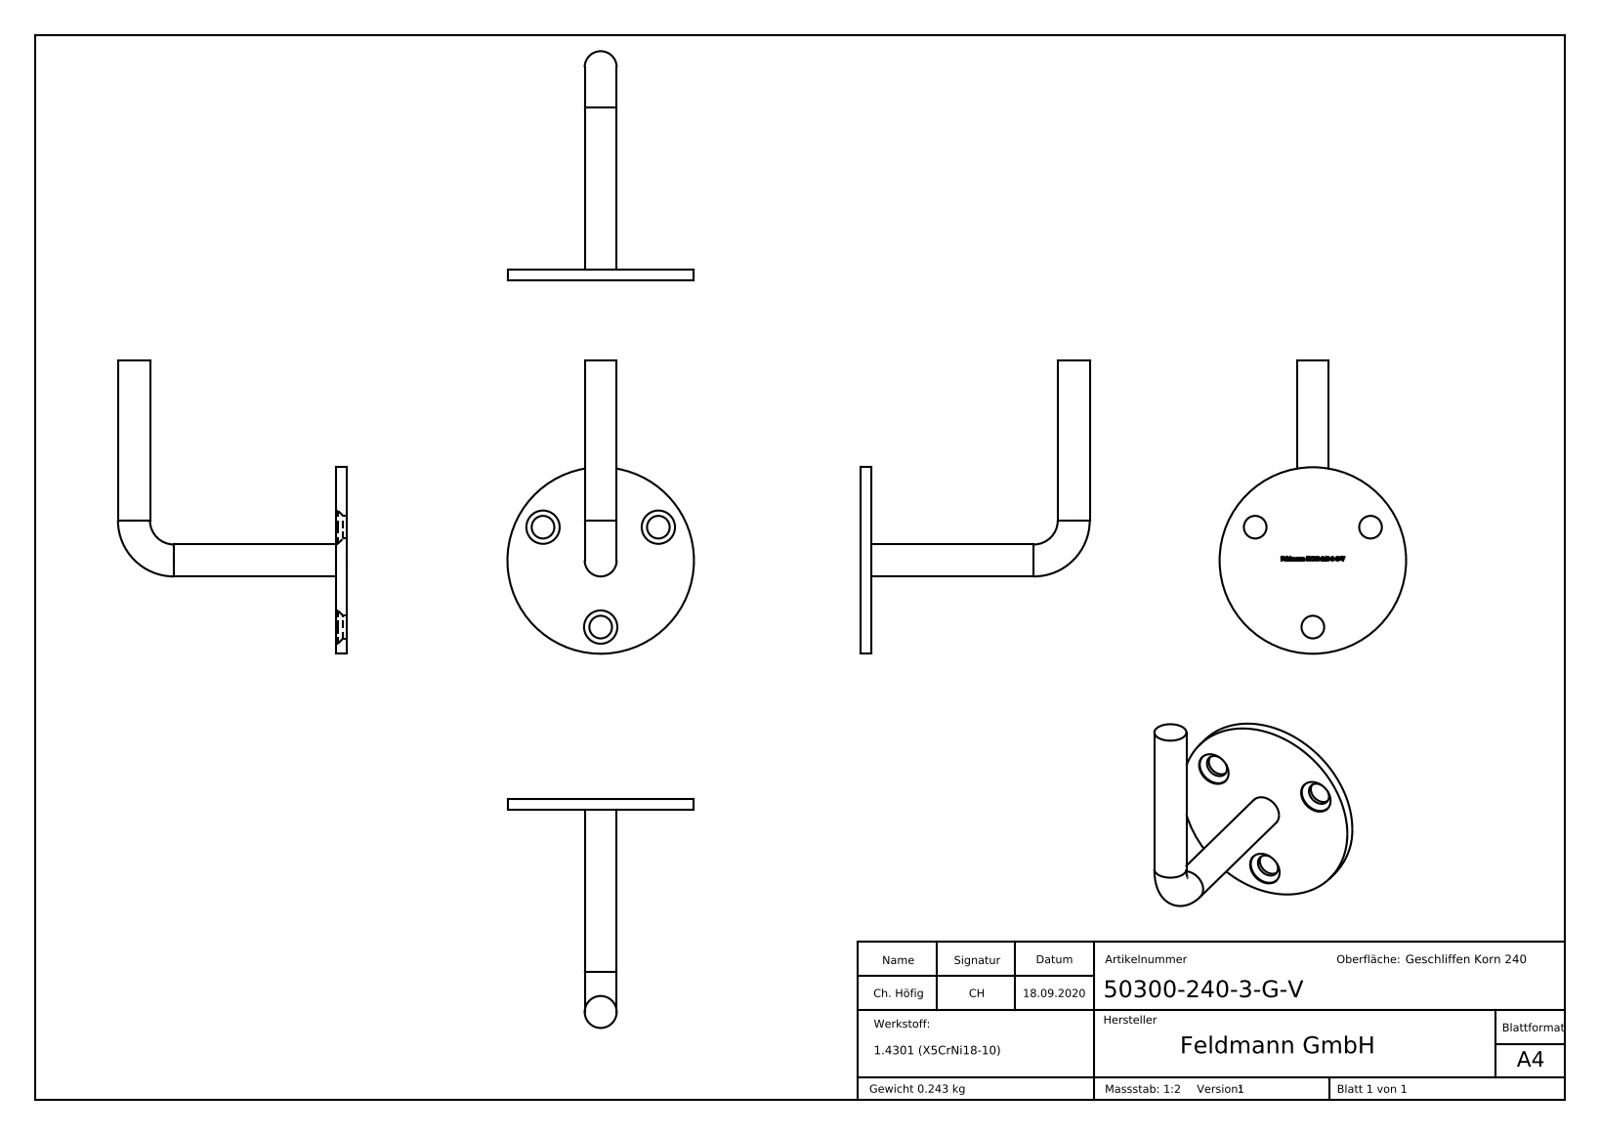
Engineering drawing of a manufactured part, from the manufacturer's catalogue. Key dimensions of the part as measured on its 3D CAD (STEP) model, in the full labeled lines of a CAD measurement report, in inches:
Part name (STEP PRODUCT): 50300-240-3-G-V
STEP written by: SolidWorks 2018 (CONFIG_CONTROL_DESIGN)
Units: inches
Bodies: 1 solid, 307 faces (146 planar, 18 cylindrical, 143 other)
Overall size (bounding box): 4.331 × 3.386 × 2.756
Volume: 1.878 in³ · Surface area: 21.64 in²
Round holes (diameter × count): ⌀0.335 ×3, ⌀0.492 ×3
Round bosses / shafts (diameter × count): ⌀0.472 ×2, ⌀2.756 ×1
Main face-to-face distances: 0.157, 0.154, 0.017, 0.015, 0.117, 0.023, 2.93, 2.935, 0.044, 0.035
Hole centre spacings: 1.705
